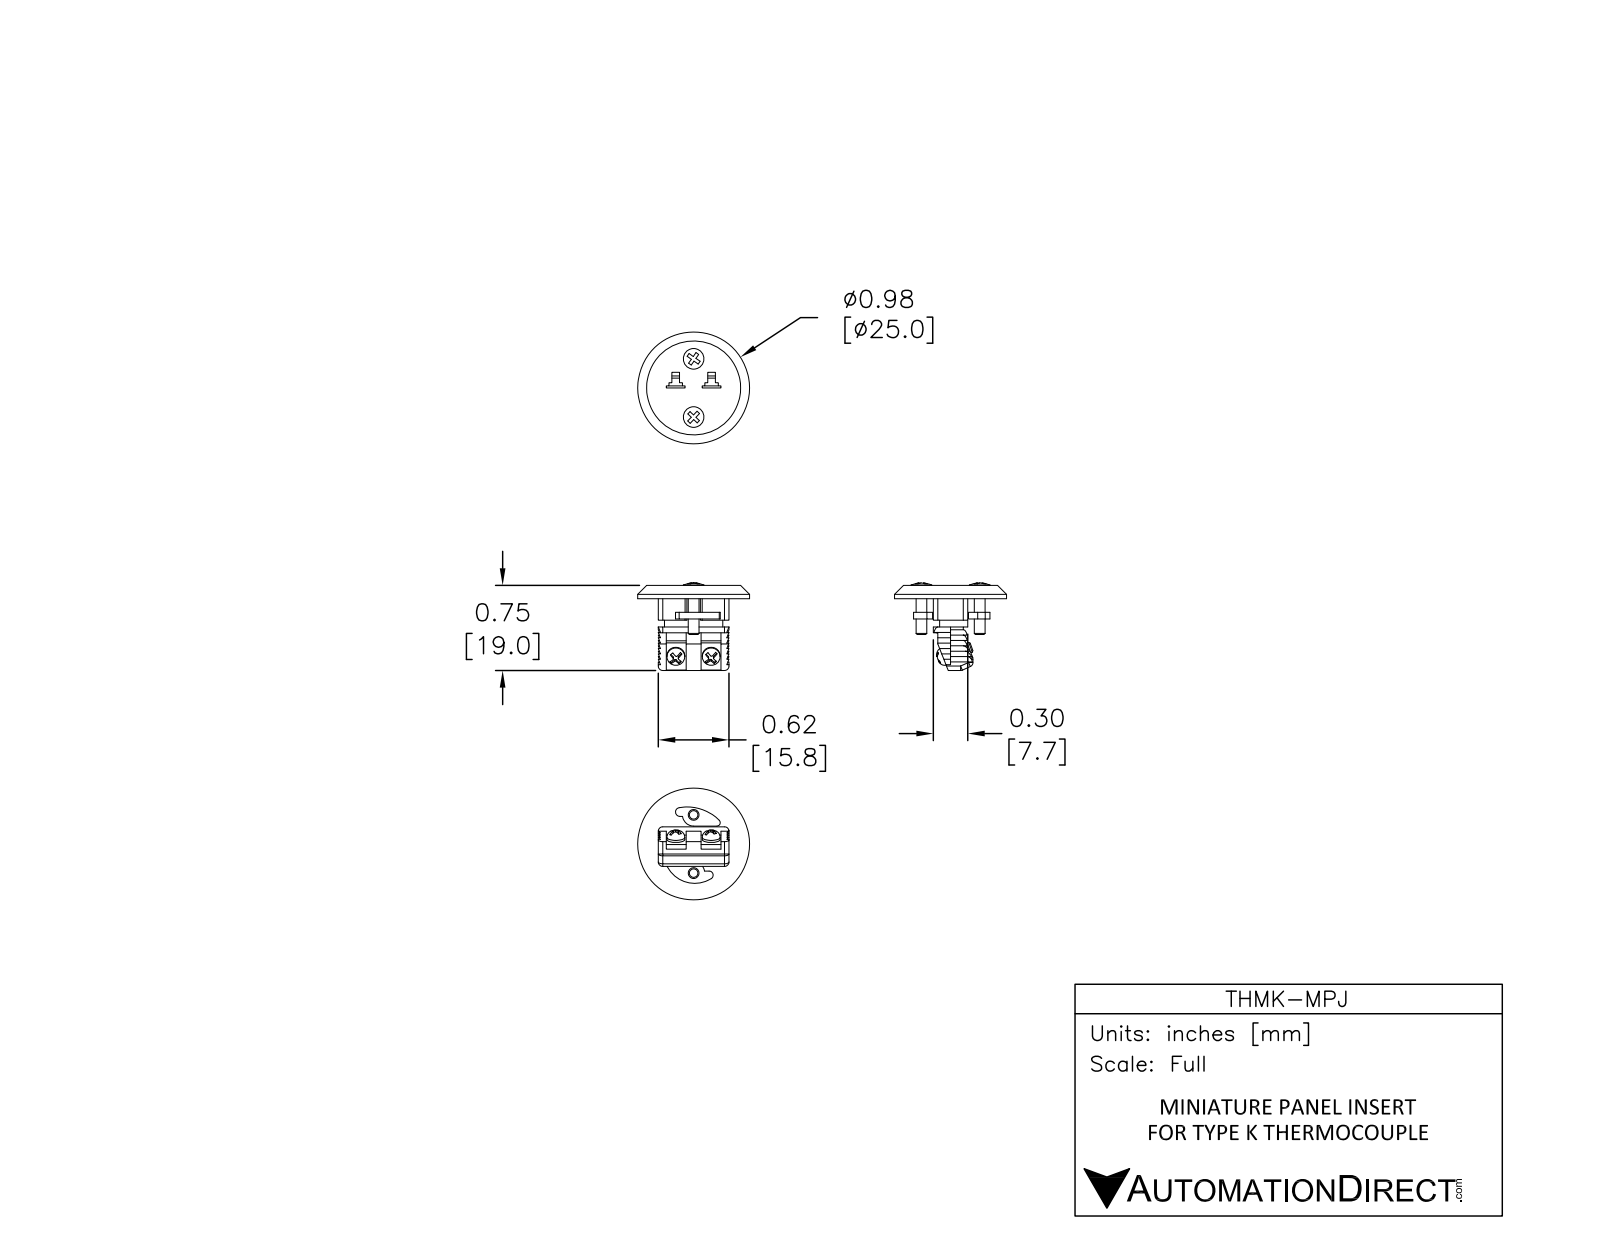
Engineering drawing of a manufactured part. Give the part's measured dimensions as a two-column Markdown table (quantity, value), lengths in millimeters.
| quantity | value |
| --- | --- |
| part name | THMK-MPJ |
| STEP written by | SolidWorks 2017 (AUTOMOTIVE_DESIGN) |
| units | millimeters |
| bodies | 1 solid, 357 faces (265 planar, 66 cylindrical, 26 other) |
| overall size | 25 × 25 × 19.57 |
| volume | 2 912 mm³ |
| surface area | 2 670 mm² |
| round bosses / shafts (diameter × count) | 4.6 × 2, 4 × 2, 2.4 × 2, 2.3 × 2, 25 × 1 |
| partial cylindrical surfaces (radius × count) | 1 × 16, 0.25 × 8, 0.75 × 2, 2.5 × 2, 0.5 × 1, 0.91 × 1, 0.98 × 1, 6.93 × 1 |
| main face-to-face distances | 2.97, 5, 1.5, 7.67, 6, 1.79, 0.46, 7.77, 0.69, 2.67 |
